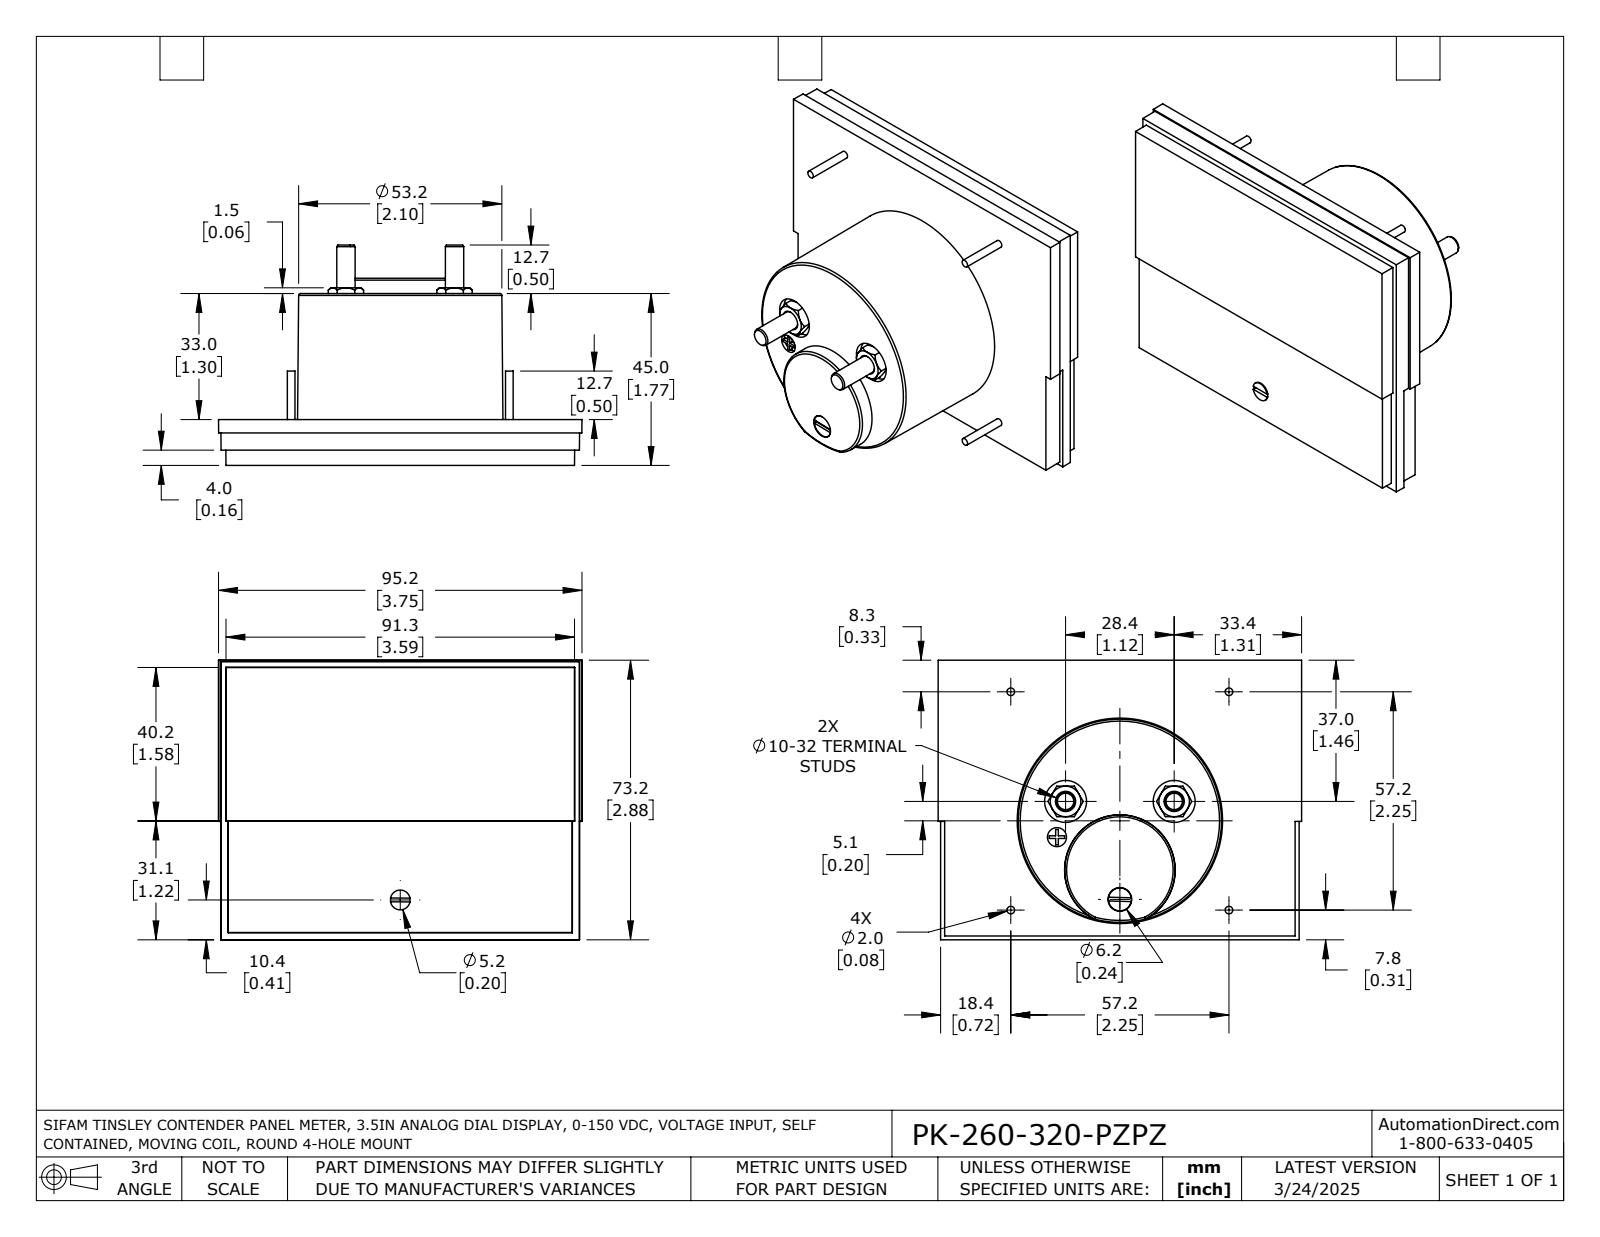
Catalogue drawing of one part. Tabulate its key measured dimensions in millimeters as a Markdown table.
| quantity | value |
| --- | --- |
| part name | PK-260-320-PZPZ |
| STEP written by | SolidWorks 2021 (AUTOMOTIVE_DESIGN) |
| units | millimeters |
| bodies | 1 solid, 163 faces (76 planar, 31 cylindrical, 56 other) |
| overall size | 95.2 × 73.2 × 57.7 |
| volume | 154 800 mm³ |
| surface area | 24 770 mm² |
| round holes (diameter × count) | 11 × 2, 5 × 1, 6.2 × 1 |
| round bosses / shafts (diameter × count) | 2 × 4, 4.8 × 2, 6 × 1, 5.2 × 1 |
| partial cylindrical surfaces (radius × count) | 2.5 × 1 |
| main face-to-face distances | 12, 0.8, 11.3, 45, 33, 44.2, 4, 1.9, 8, 37 |
| hole center spacings | 29.3, 9.6, 23.2, 28.4, 32.1 |
